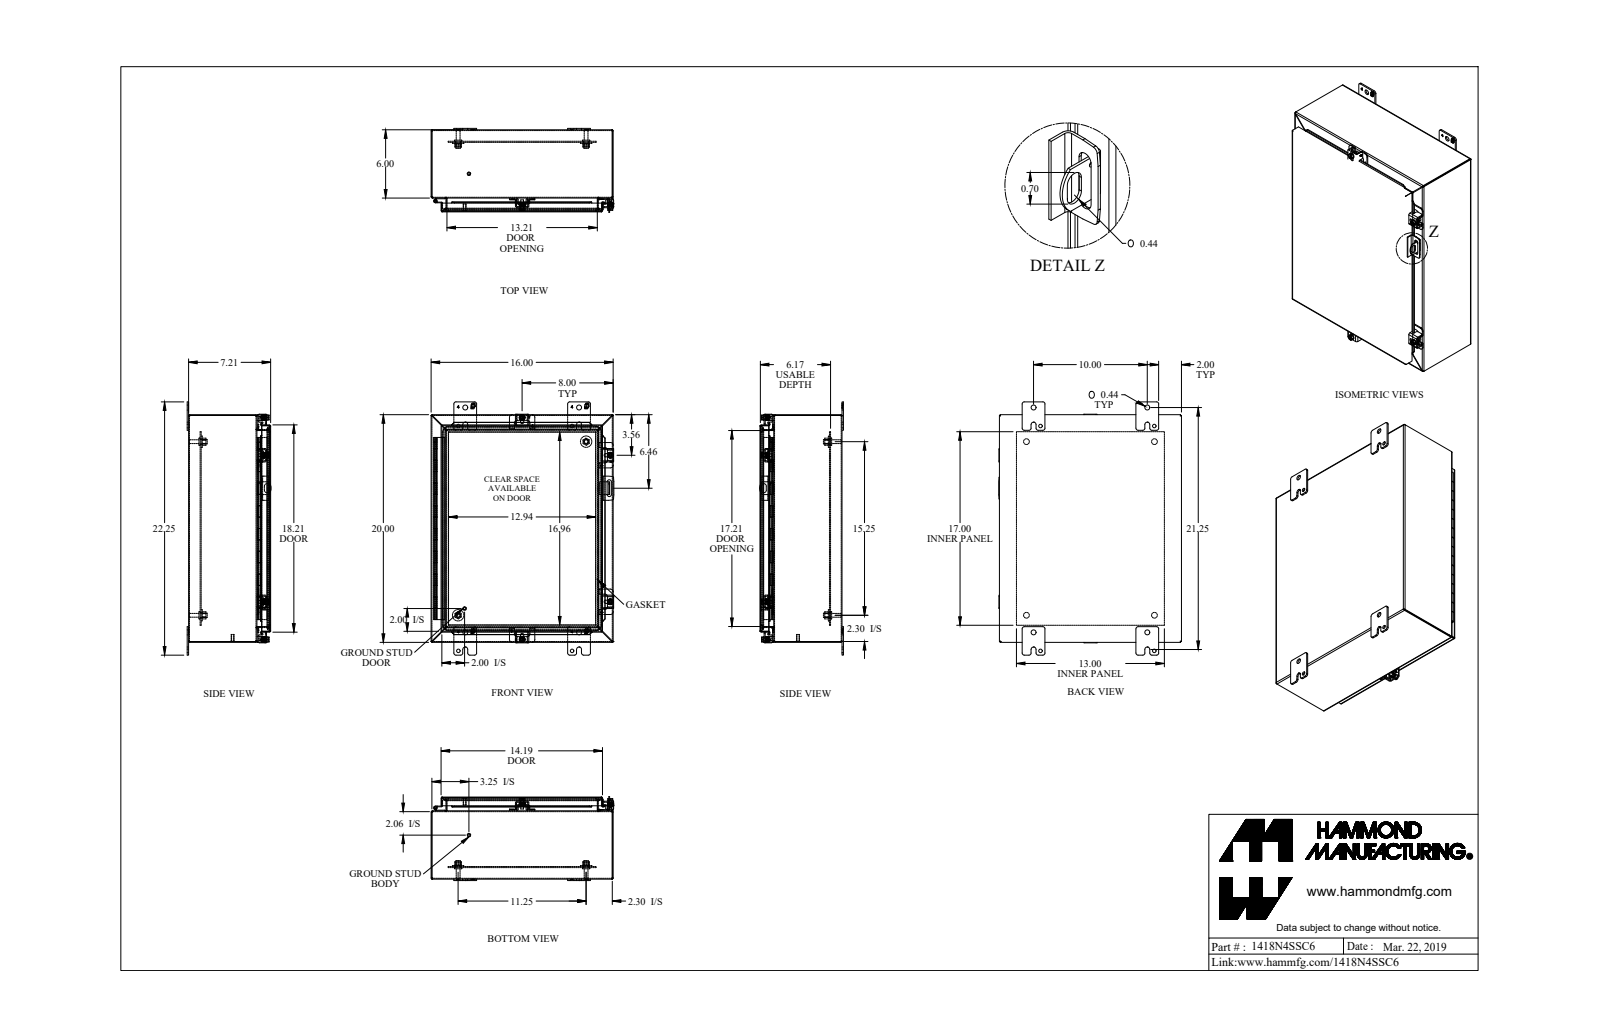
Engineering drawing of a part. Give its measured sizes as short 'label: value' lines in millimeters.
name: 1418N4SSC6_Default
written by: SolidWorks 2019 (CONFIG_CONTROL_DESIGN)
unit: mm
bodies: 39 solids, 1454 faces (905 planar, 457 cylindrical, 92 other)
size: 565.2 × 408 × 187.3
volume: 1 998 000 mm³; area: 2 081 000 mm²
holes: 4× ⌀5.4, 4× ⌀6.7, 4× ⌀8, 4× ⌀9.5, 4× ⌀11.1, 4× ⌀12.7, 2× ⌀7.8, 2× ⌀11.3, 1× ⌀3.2, 1× ⌀4.7
bosses: 4× ⌀16.5, 4× ⌀12.7, 4× ⌀9.9, 4× ⌀9.5, 4× ⌀8.4, 4× ⌀6.2, 2× ⌀25.4, 2× ⌀8
rounds: 26× R4.8, 24× R0.9, 24× R2.7, 21× R1.2, 21× R3.6, 20× R6.4, 8× R1.1, 8× R3.2
face distances: 1.8, 1.8, 179.5, 181.3, 181.3, 183.1, 23.8, 25.6, 404.6, 2.4
hole spacings: 463.9, 152.7, 254, 61.8, 77.9, 280.4, 285.8, 387.4
